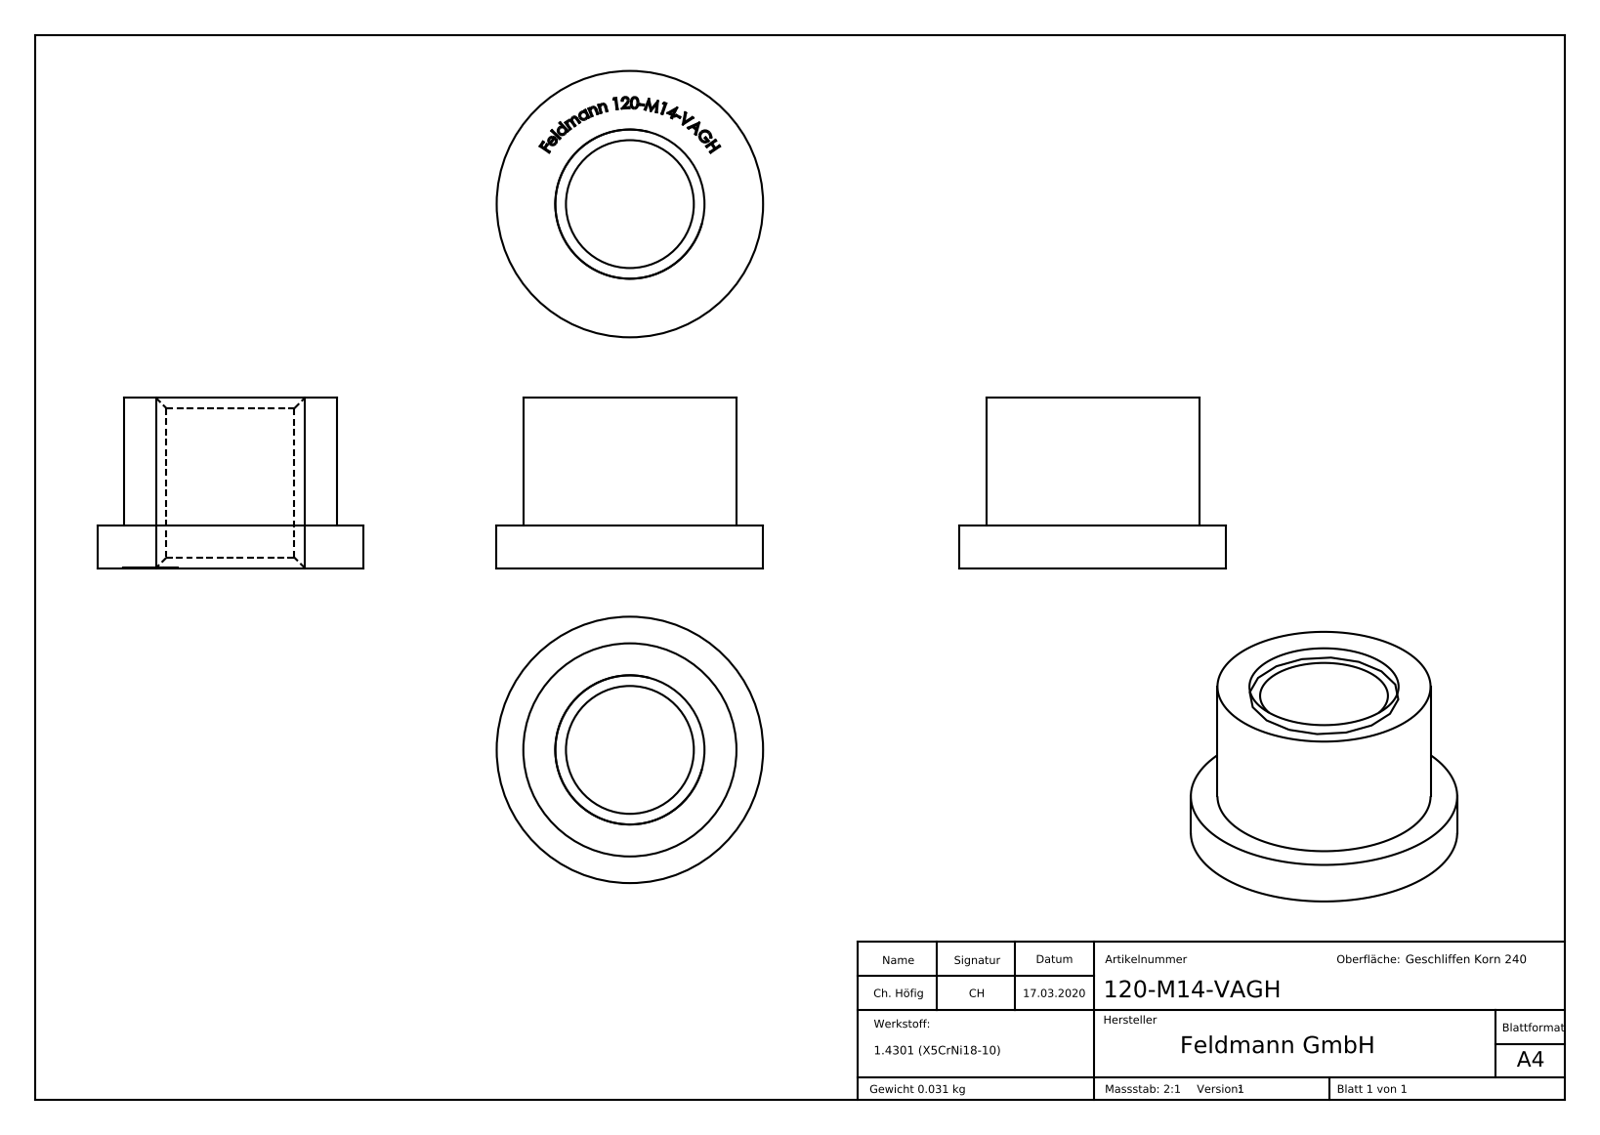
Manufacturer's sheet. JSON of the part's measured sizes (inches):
{"part_name": "120-M14-VAGH", "step_written_by": "SolidWorks 2015 (CONFIG_CONTROL_DESIGN)", "units": "inches", "bodies": {"solids": 1, "faces": 246, "planar": 169, "cylindrical": 3, "other": 74}, "overall_size": [0.984, 0.984, 0.63], "volume_in3": 0.237, "surface_area_in2": 3.711, "round_holes": [[0.472, 1]], "round_bosses_or_shafts": [[0.984, 1], [0.787, 1]], "face_to_face_distances": [0.157, 0.63, 0.472, 0.154, 0.626, 0.025, 0.021, 0.021, 0.029, 0.017]}
